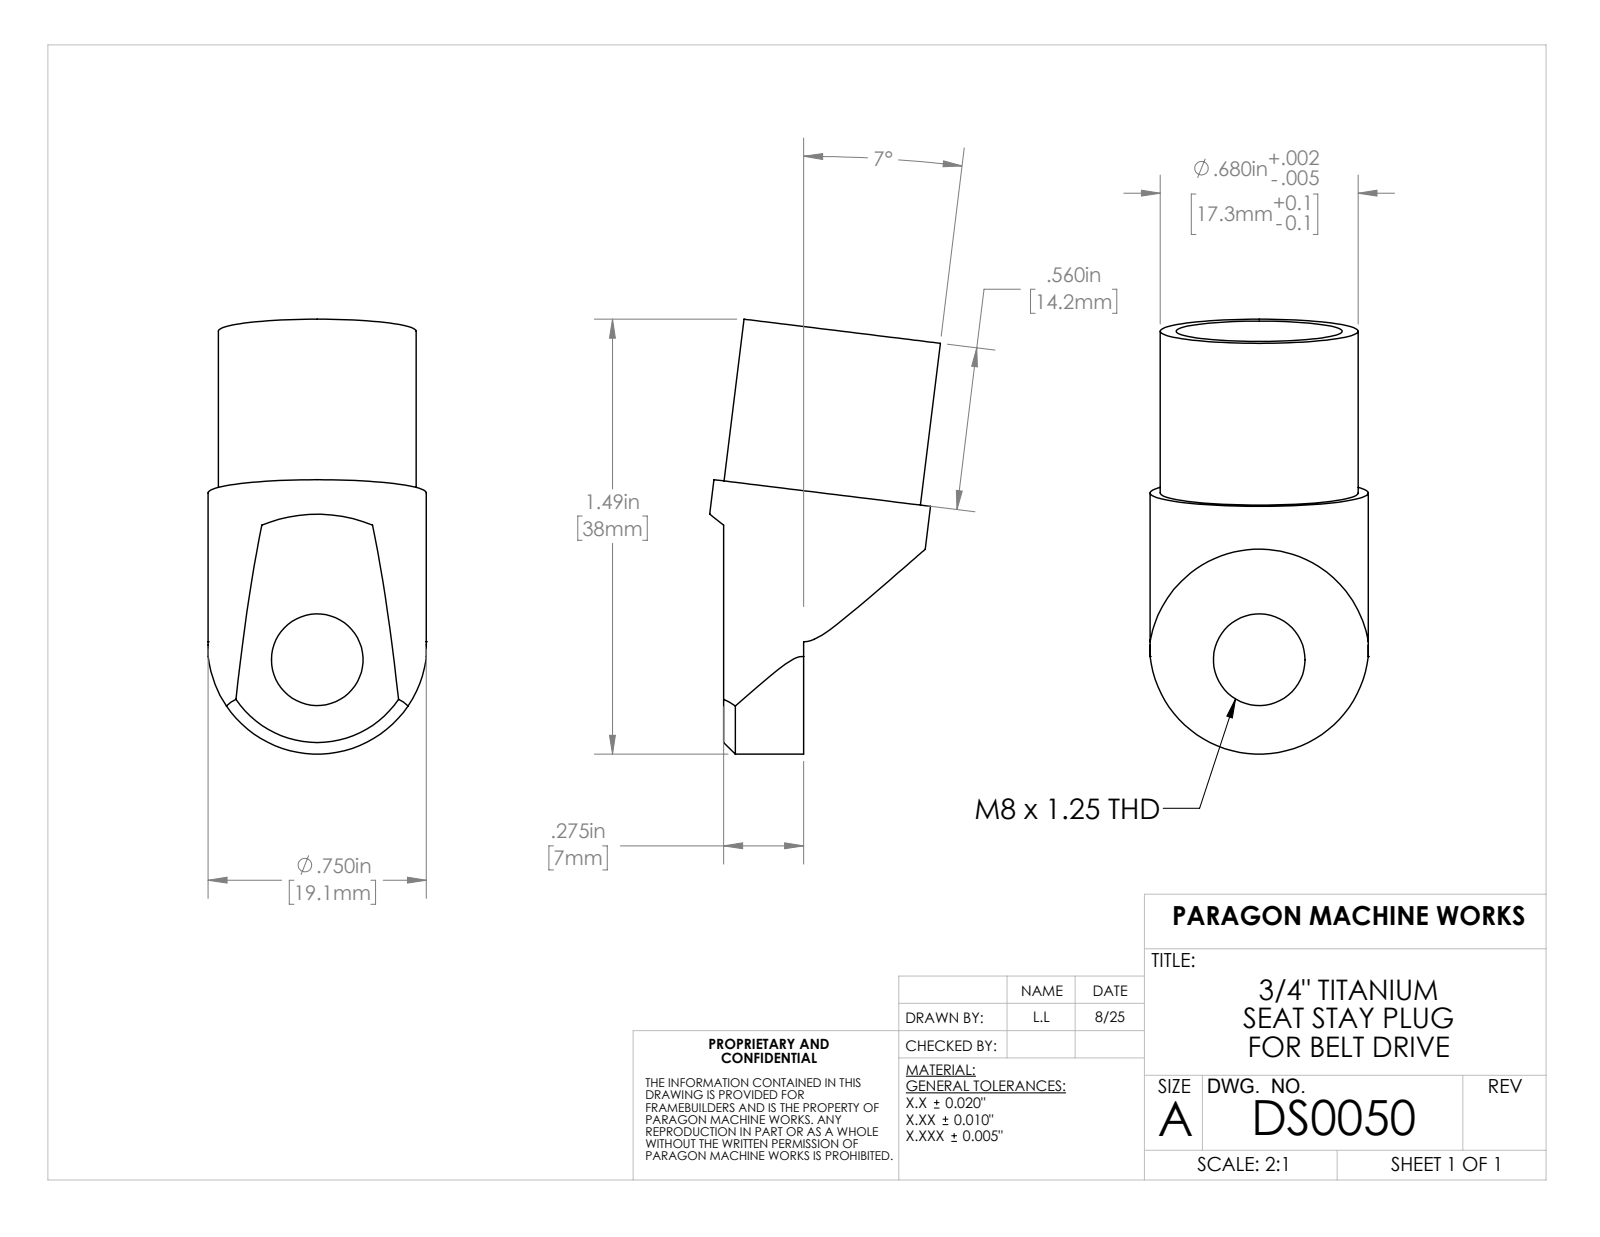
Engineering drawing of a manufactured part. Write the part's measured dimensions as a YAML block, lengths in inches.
part_name: "DS0050"
step_written_by: "SolidWorks 2023 (AUTOMOTIVE_DESIGN)"
units: inches
bodies: {solids: 1, faces: 20, planar: 6, cylindrical: 11, other: 3}
overall_size: [1.494, 0.792, 0.75]
volume: 0.223
surface_area: 5.139
round_holes:
  - {diameter: 0.315, count: 1}
  - {diameter: 0.571, count: 1}
round_bosses_or_shafts:
  - {diameter: 0.75, count: 1}
  - {diameter: 0.68, count: 1}
partial_cylinders:
  - {radius: 0.377, count: 1}
  - {radius: 0.38, count: 1}
  - {radius: 0.5, count: 1}
face_to_face_distances: [0.275, 0.56]
